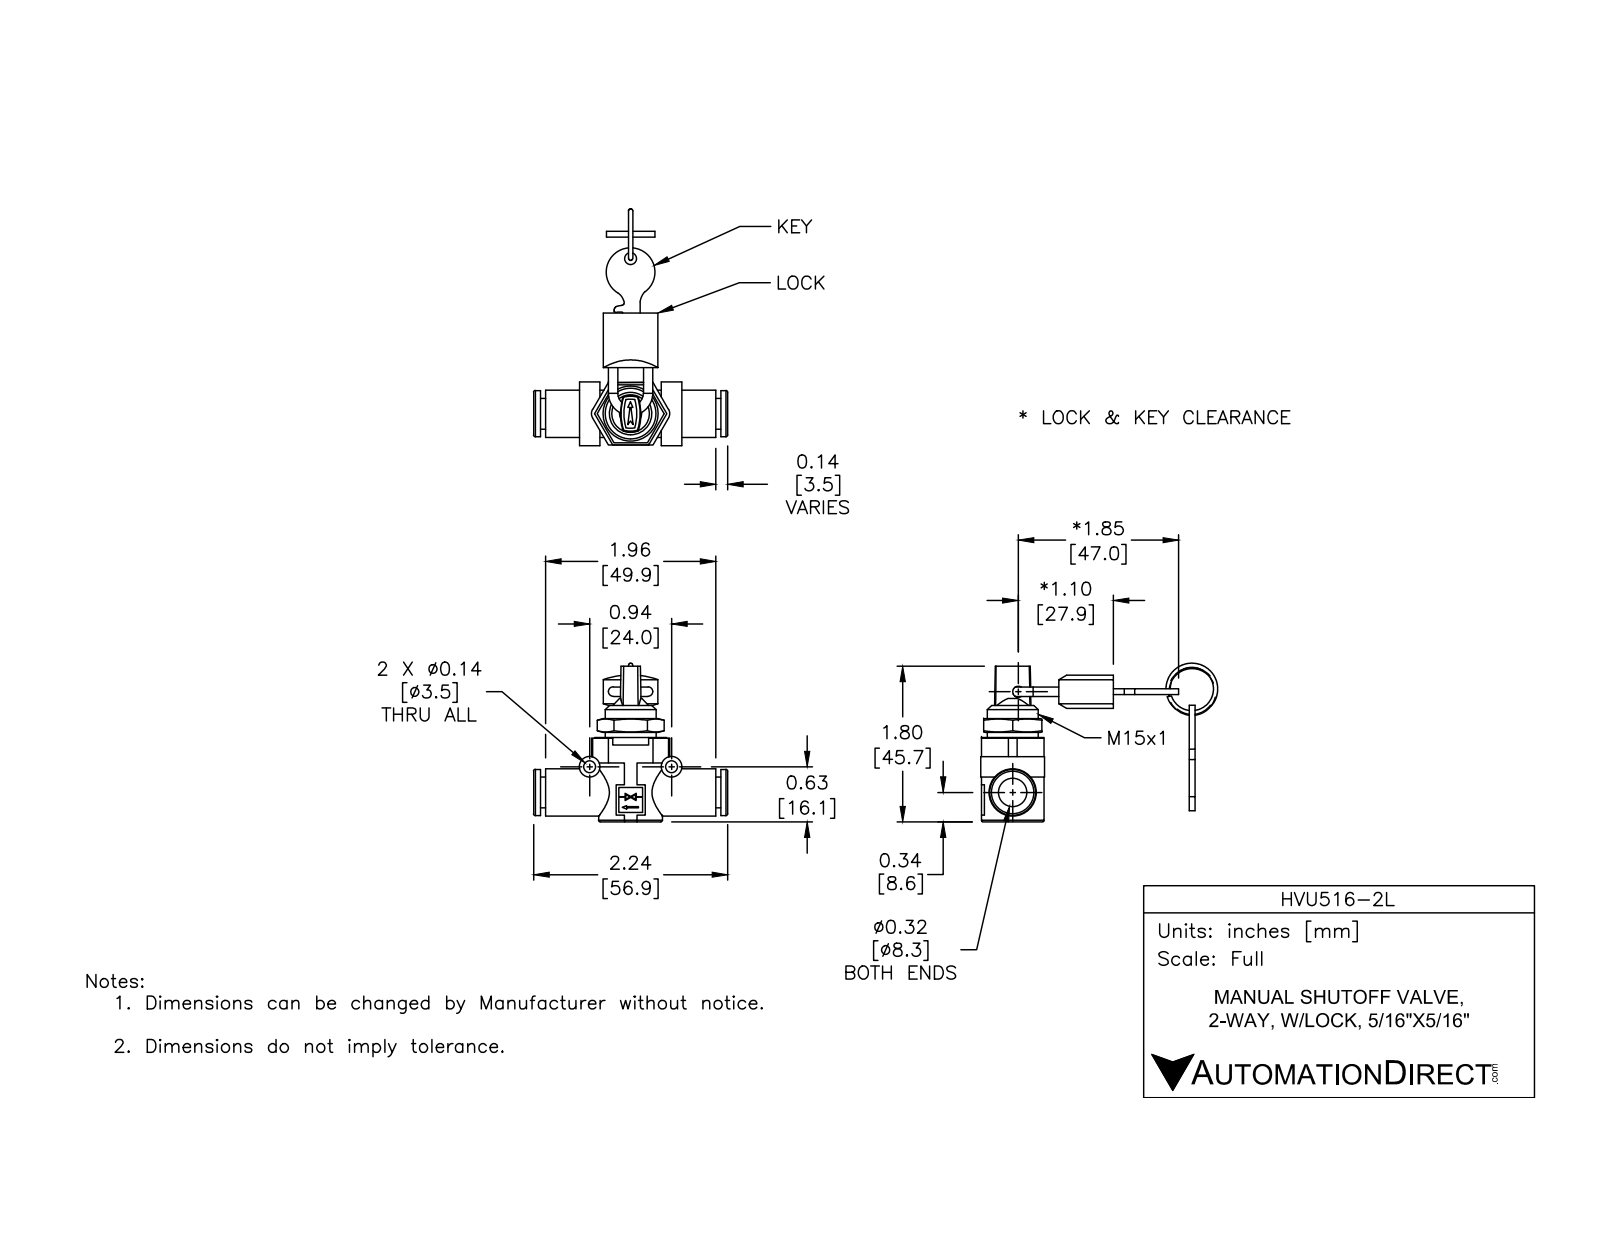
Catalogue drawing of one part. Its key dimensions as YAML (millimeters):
part_name: "HVU516-2L"
step_written_by: "SolidWorks 2015 (CONFIG_CONTROL_DESIGN)"
units: millimeters
bodies: {solids: 11, faces: 226, planar: 125, cylindrical: 73, other: 28}
overall_size: [69.44, 56.9, 46.53]
volume: 17640
surface_area: 11562
round_holes:
  - {diameter: 3.5, count: 4}
  - {diameter: 3.25, count: 1}
  - {diameter: 8, count: 1}
  - {diameter: 8.25, count: 1}
  - {diameter: 9, count: 1}
  - {diameter: 11, count: 1}
  - {diameter: 13.47, count: 1}
round_bosses_or_shafts:
  - {diameter: 14.25, count: 2}
  - {diameter: 6, count: 2}
  - {diameter: 2.75, count: 2}
  - {diameter: 18.7, count: 1}
  - {diameter: 14.9, count: 1}
  - {diameter: 14, count: 1}
  - {diameter: 13.9, count: 1}
  - {diameter: 13.5, count: 1}
partial_cylinders:
  - {radius: 0.5, count: 2}
  - {radius: 2.5, count: 2}
  - {radius: 4.05, count: 2}
  - {radius: 5.58, count: 2}
  - {radius: 7.03, count: 2}
  - {radius: 14.56, count: 2}
  - {radius: 24.18, count: 2}
face_to_face_distances: [1.7, 1.5, 37.3, 39, 2, 7.05, 4.01, 26.24, 30.25, 11.06]
hole_center_spacings: [19.1, 25.09, 7.17, 24, 29.57, 45.44, 50.98, 60.33]
